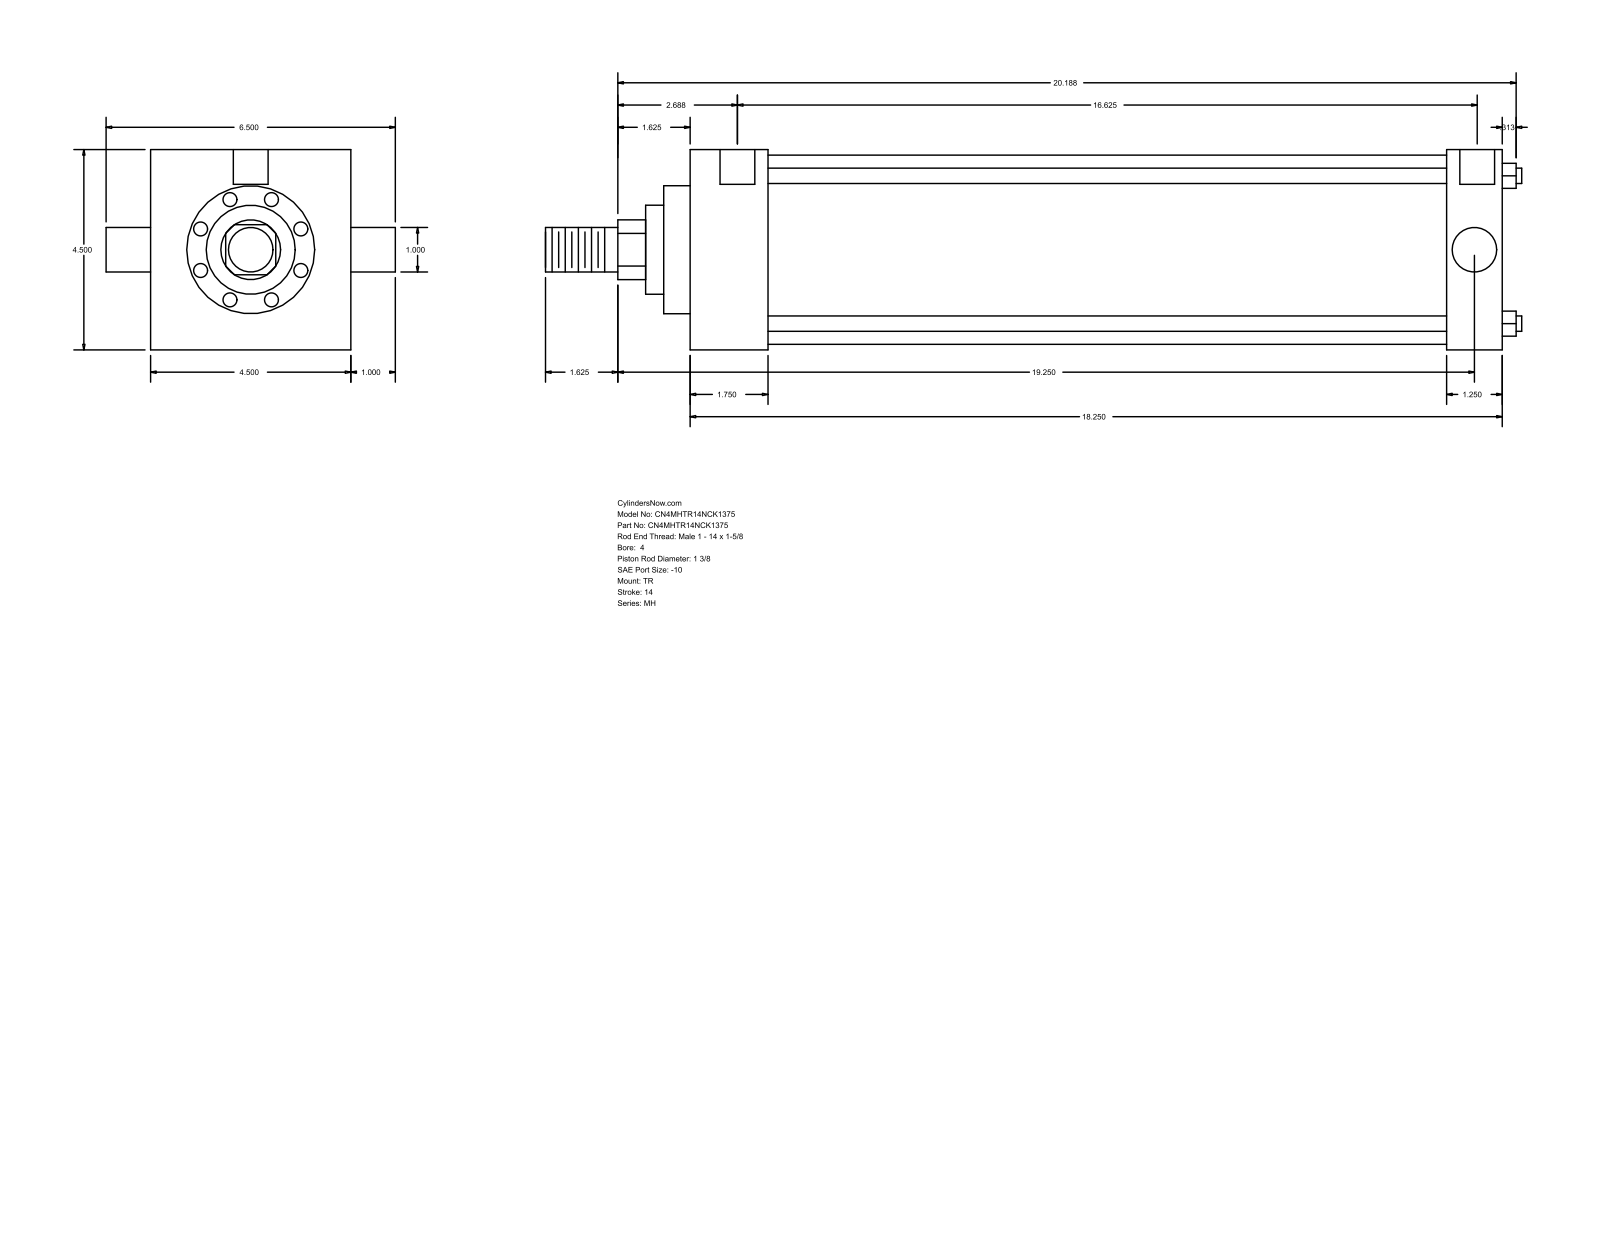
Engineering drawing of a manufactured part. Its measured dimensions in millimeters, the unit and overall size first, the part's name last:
Units: millimetres
Overall size (bounding box): 557.21 × 165.1 × 114.3
Round holes (diameter × count): ⌀8.73 ×3, ⌀19.84 ×2
Round bosses / shafts (diameter × count): ⌀8.76 ×4, ⌀25.4 ×2, ⌀107.95 ×1, ⌀73.03 ×1, ⌀50.8 ×1, ⌀34.92 ×1
Partial cylindrical surfaces — rounded edges, fillets, slot ends (radius × count): R17.06 ×1
Main face-to-face distances: 114.3, 463.55, 44.45, 419.1, 431.8, 387.35, 31.75, 15.08, 59.53, 446.88
Hole centre spacings: 1.58, 1.59, 422.28, 423.86, 423.87, 425.45
Bodies: 0 solids, 86 faces (61 planar, 25 cylindrical, 0 other)
Part name (STEP PRODUCT): MH_TR__0400_1.375
STEP written by: GSSL Pune (CONFIG_CONTROL_DESIGN)
